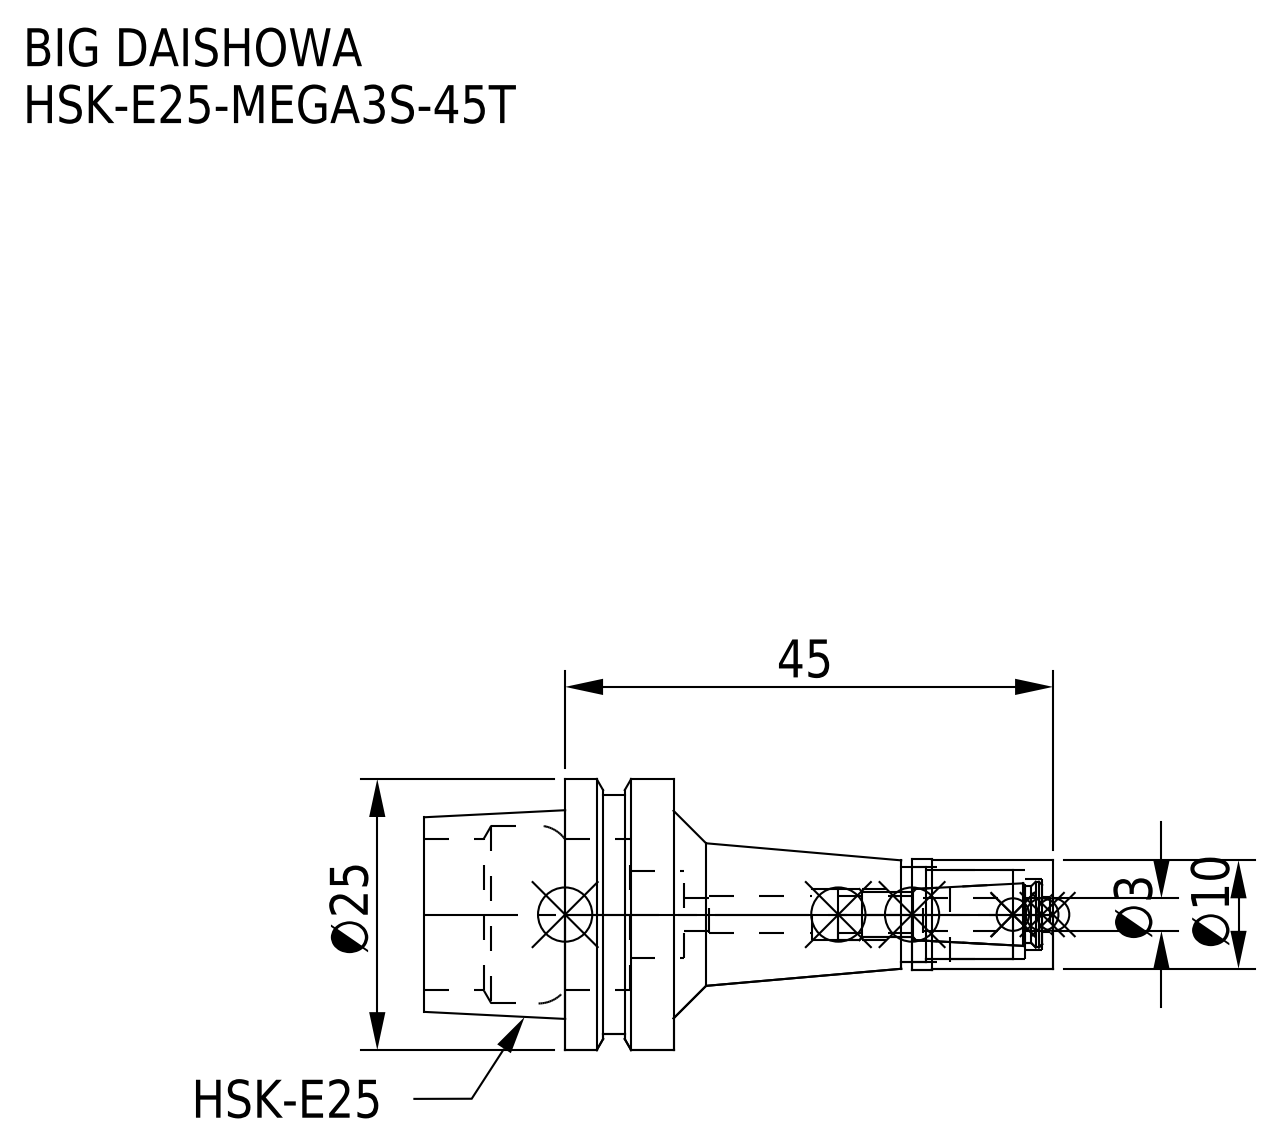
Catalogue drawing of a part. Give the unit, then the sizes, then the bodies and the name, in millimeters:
Units: millimetres
Overall size (bounding box): 58 × 25 × 25
Round holes (diameter × count): ⌀3 ×1, ⌀3.3 ×1, ⌀3.4 ×1, ⌀4.7 ×1, ⌀6.6 ×1, ⌀8 ×1, ⌀8.2 ×1, ⌀8.7 ×1, ⌀14 ×1, ⌀16.4 ×1
Round bosses / shafts (diameter × count): ⌀25 ×1, ⌀22 ×1, ⌀10.3 ×1, ⌀10 ×1
Main face-to-face distances: 10, 13, 4.05, 5.95, 23, 18.95, 45, 35, 39.05, 58
Volume: 7 664 mm³ · Surface area: 5 878 mm²
Bodies: 2 solids, 74 faces (18 planar, 38 cylindrical, 18 other)
Part name (STEP PRODUCT): HSK-E25-MEGA3S-45T-030.stp; MGN3S_1.stp; HSK-E25-MEGA3S-45T_1.stp; DXF_TEMP_ASSY_ASM_4_ASM.stp (+3 more)
STEP written by: SolidWorks 2019 (CONFIG_CONTROL_DESIGN)
